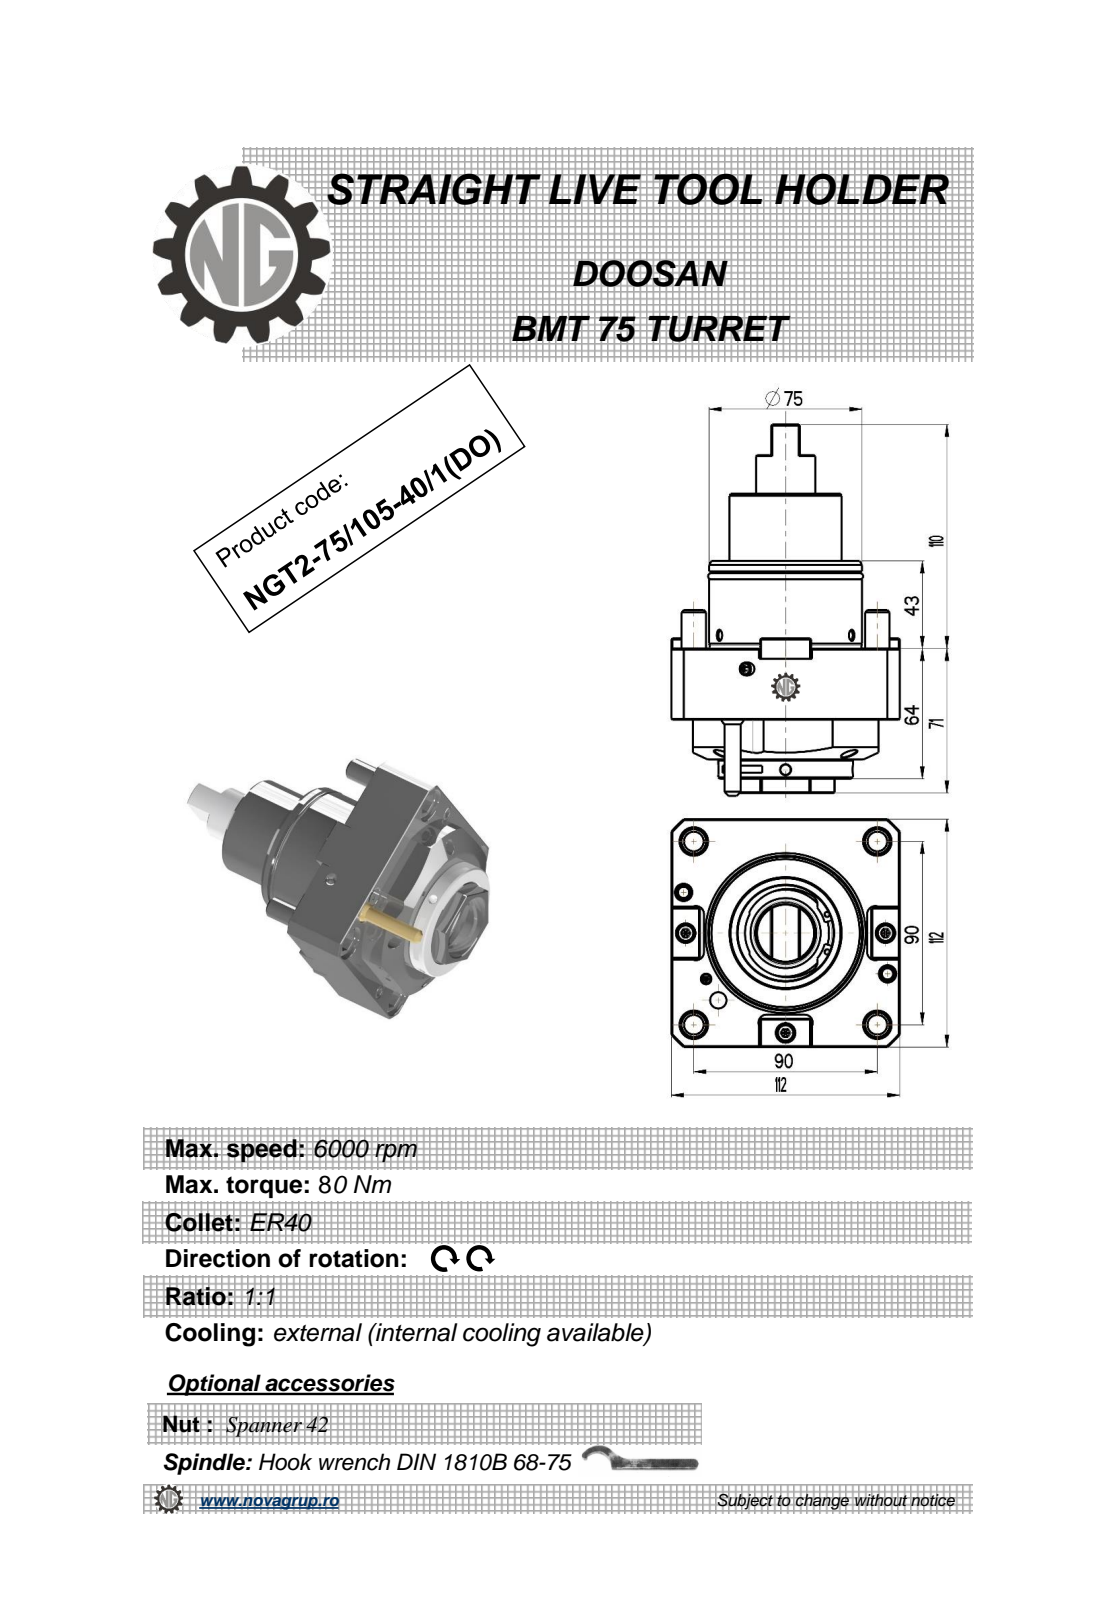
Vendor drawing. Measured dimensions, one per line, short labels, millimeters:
name: NGT2_75_105_40_1_DO
written by: PRO/ENGINEER BY PARAMETRIC TECHNOLOGY CORPORATION, 2010280 (CONFIG_CONTROL_DESIGN)
unit: mm
bodies: 2 solids, 187 faces (74 planar, 57 cylindrical, 56 other)
size: 182.34 × 112 × 112
volume: 898 665 mm³; area: 78 168 mm²
holes: 3× ⌀5, 1× ⌀3, 1× ⌀8, 1× ⌀36.2, 1× ⌀42
bosses: 4× ⌀12, 1× ⌀75, 1× ⌀70, 1× ⌀66, 1× ⌀55, 1× ⌀29, 1× ⌀8
rounds: 2× R0.8, 1× R6, 1× R24, 1× R51, 1× R75
face distances: 112, 35, 54.5, 19.5, 10.5, 101.5, 76, 29, 33, 43
hole spacings: 17.01, 46.67, 55.03
